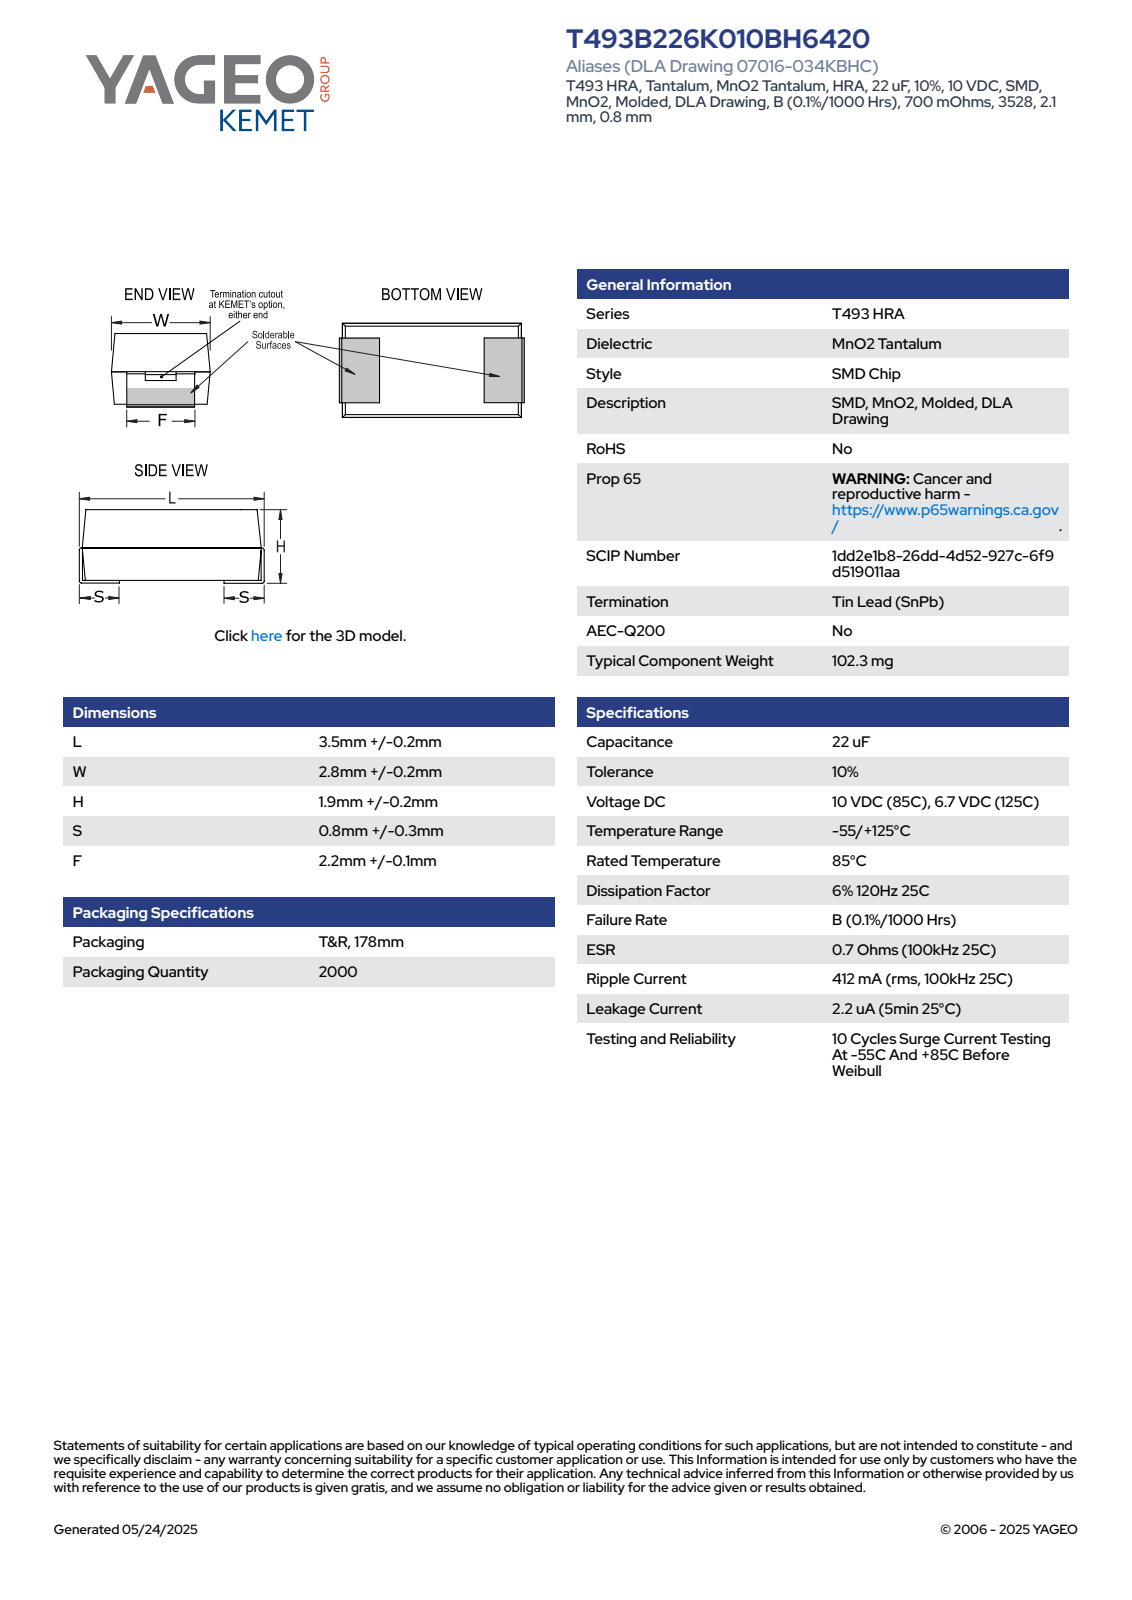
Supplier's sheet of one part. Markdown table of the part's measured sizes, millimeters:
| quantity | value |
| --- | --- |
| part name | CTSM_3528_L3.70W3H2.10S0.8F2.2; CTSM_Case_Anode_22; CTSM_Case_Cathode_22; CTSM_Case_Top_22 (+1 more) |
| STEP written by | SolidWorks 2014 (AUTOMOTIVE_DESIGN) |
| units | millimeters |
| bodies | 7 solids, 94 faces (90 planar, 4 cylindrical, 0 other) |
| overall size | 3.7 × 3 × 2.1 |
| volume | 21 mm³ |
| surface area | 82 mm² |
| main face-to-face distances | 1.07, 0.9, 1.97, 2.98, 3.43, 3.57, 2.1, 1.03, 1, 2.07 |
